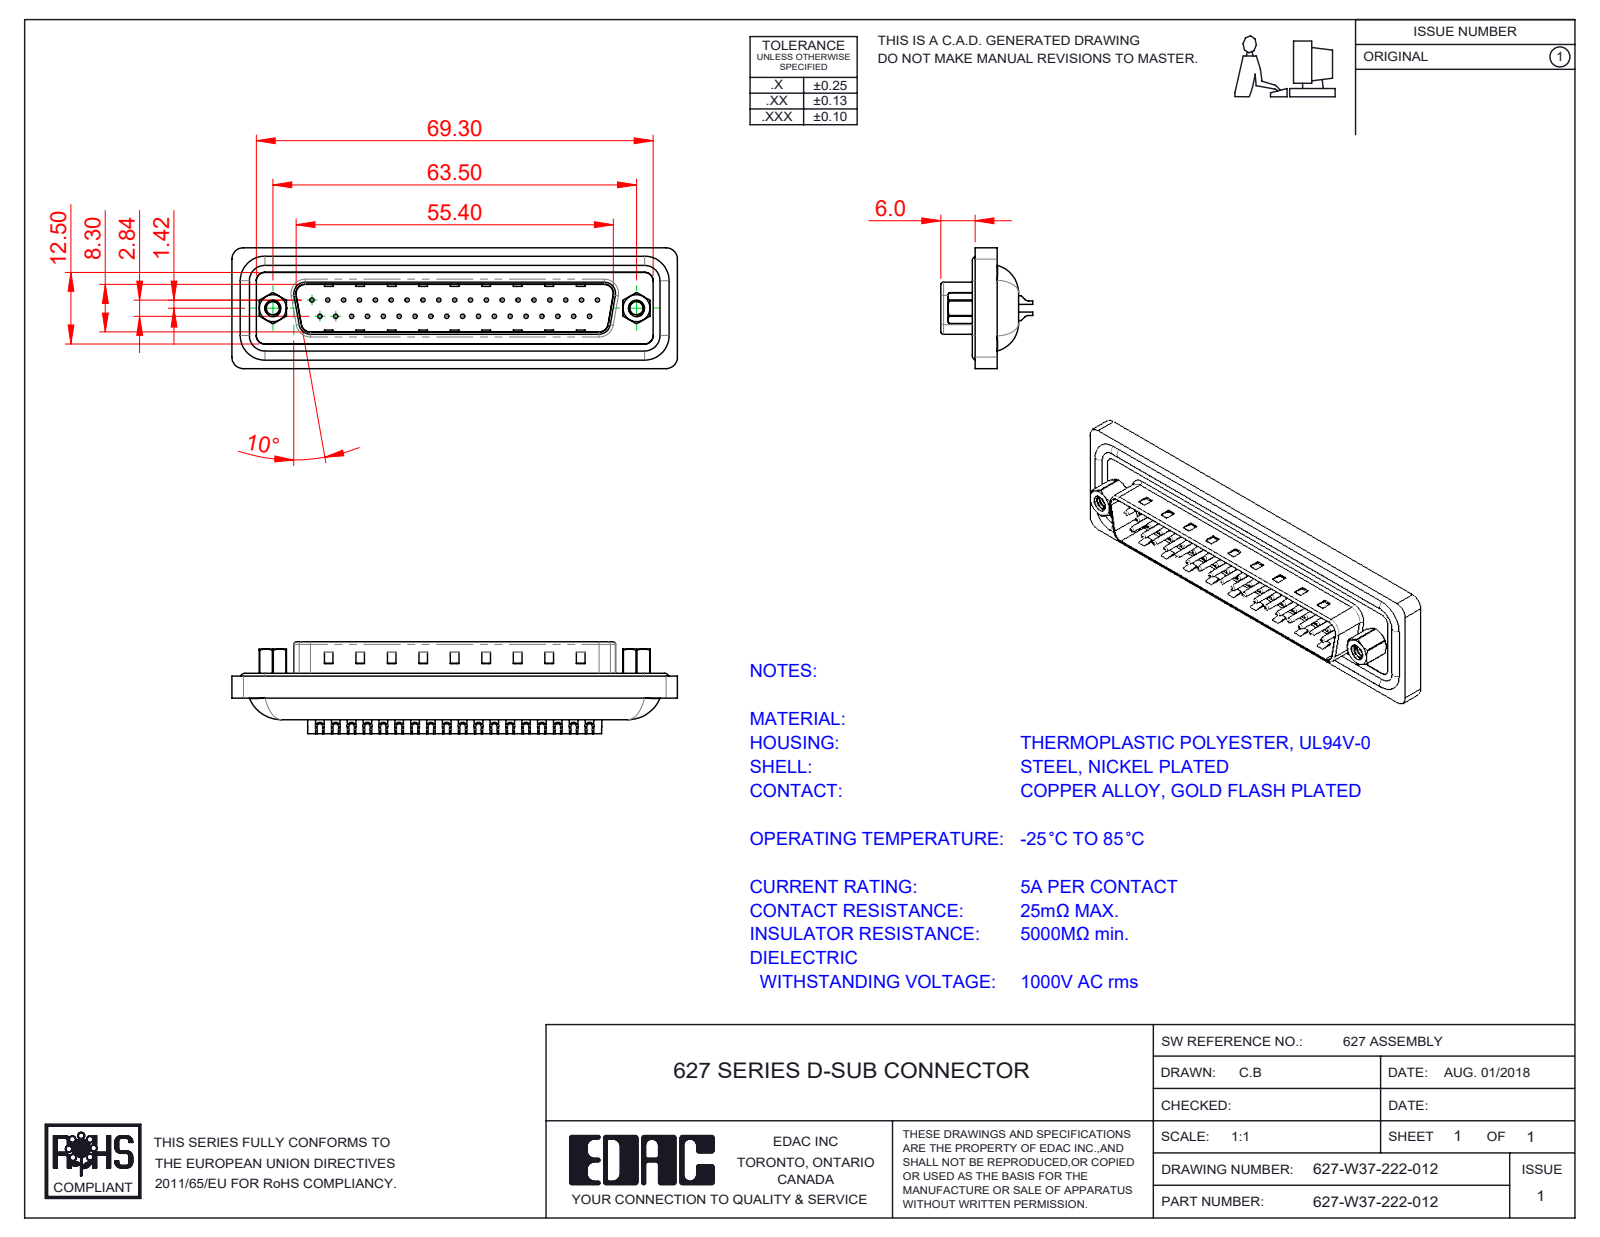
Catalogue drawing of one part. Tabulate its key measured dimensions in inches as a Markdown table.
| quantity | value |
| --- | --- |
| part name | 627W Contact Row 1_22; 627W Shell Front_37 Contacts; 627W Contact Row 2_22; 627W Waterproof Housing_37 Contacts (+4 more) |
| STEP written by | SolidWorks 2023 (CONFIG_CONTROL_DESIGN) |
| units | inches |
| bodies | 45 solids, 1999 faces (570 planar, 890 cylindrical, 539 other) |
| overall size | 3.063 × 0.831 × 0.64 |
| volume | 0.584 in³ |
| surface area | 22.66 in² |
| round holes (diameter × count) | 0.03 × 37, 0.039 × 37, 0.059 × 37, 0.063 × 37, 0.079 × 37, 0.089 × 2, 0.09 × 2, 0.157 × 2, 0.189 × 2, 0.197 × 2 |
| round bosses / shafts (diameter × count) | 0.059 × 9, 0.063 × 4, 0.193 × 2, 0.11 × 2 |
| partial cylindrical surfaces (radius × count) | 0.079 × 16, 0.059 × 14, 0.02 × 8, 0.106 × 6, 0.035 × 4, 0.063 × 4, 0.169 × 4, 0.016 × 2 |
| main face-to-face distances | 0.03, 0.016, 0.161, 0.043, 0.108, 0.181, 0.148, 0.222, 0.608, 0.579 |
| hole center spacings | 0.124, 0.109, 0.218, 0.327, 0.198, 0.398, 0.436, 0.503 |
